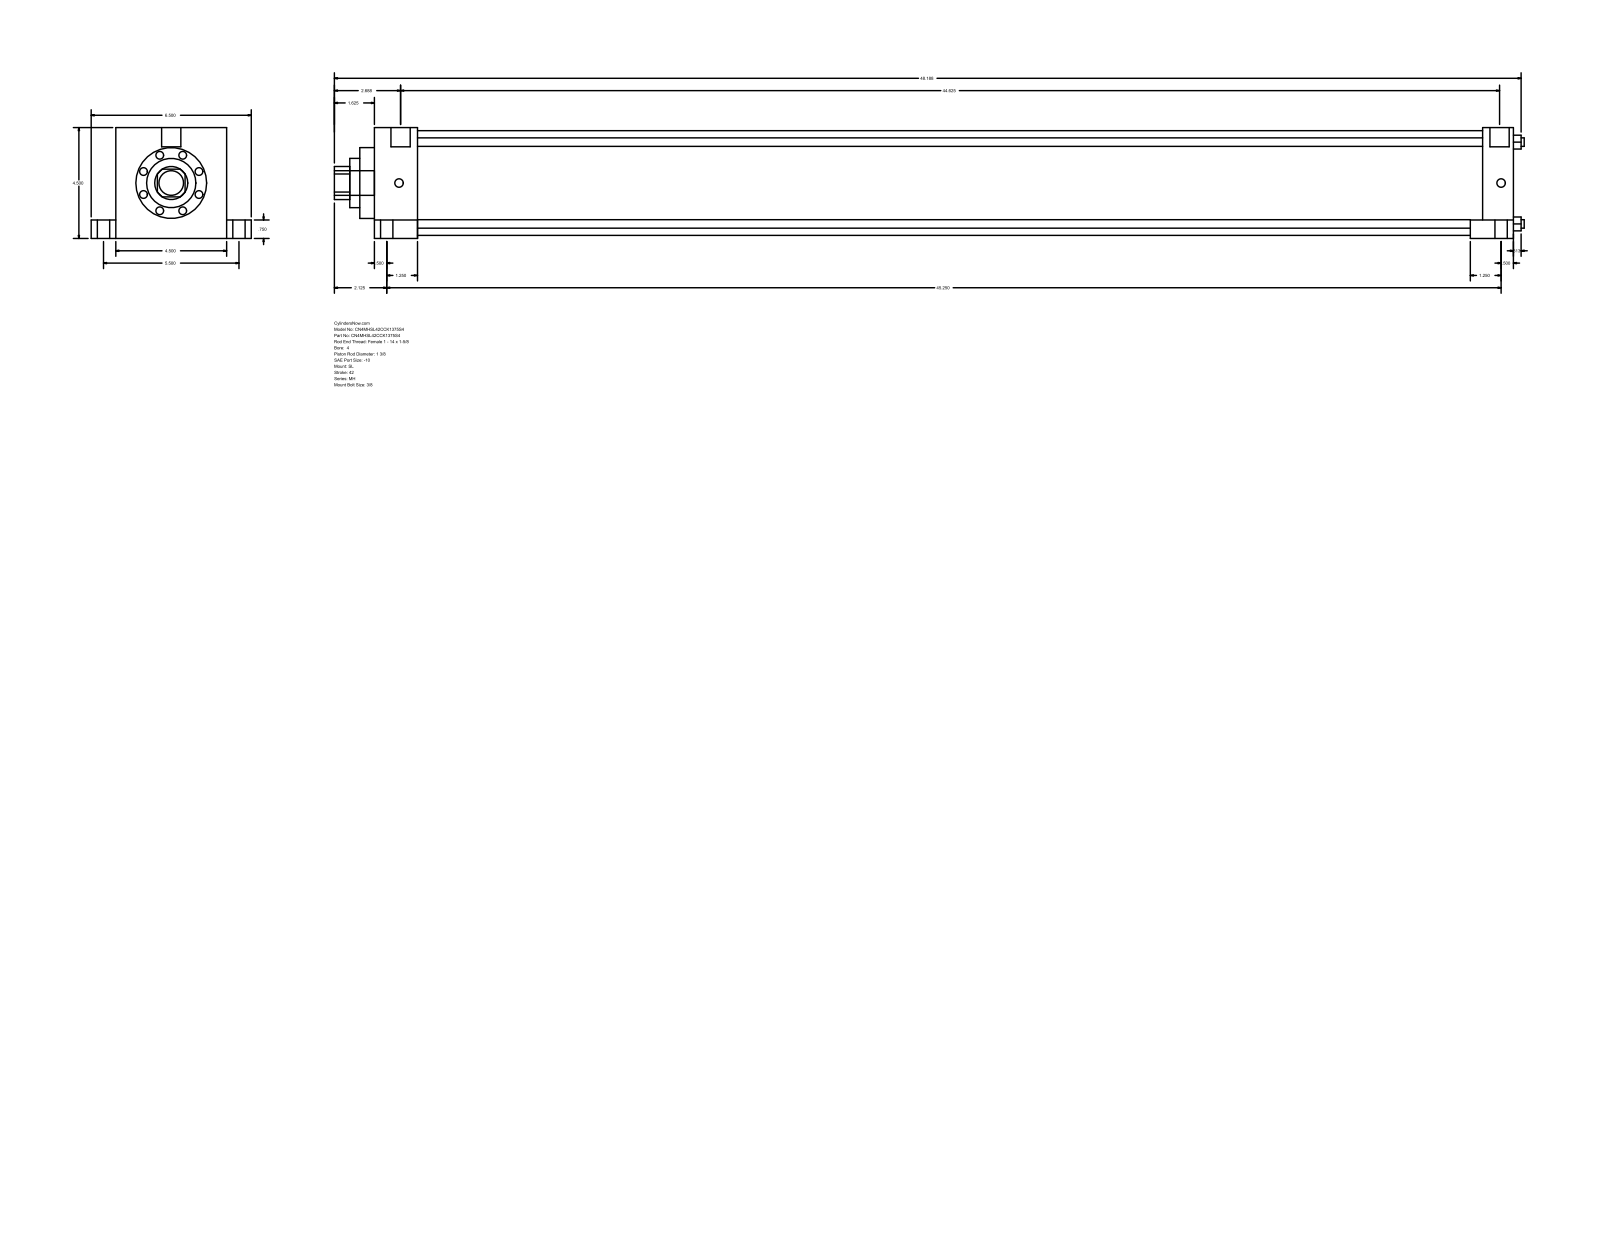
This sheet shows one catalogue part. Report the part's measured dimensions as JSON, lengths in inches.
{"part_name": "MH_SL__0400_1.375", "step_written_by": "GSSL Pune (CONFIG_CONTROL_DESIGN)", "units": "inches", "bodies": {"solids": 0, "faces": 110, "planar": 77, "cylindrical": 33, "other": 0}, "overall_size": [48.313, 6.5, 4.5], "round_holes": [[0.345, 4], [1.375, 1], [2, 1], [2.875, 1], [4.25, 1]], "round_bosses_or_shafts": [[0.75, 4], [0.5, 4], [0.344, 4], [0.781, 2], [1, 1]], "partial_cylinders_radius": [[0.672, 1]], "face_to_face_distances": [4.5, 46.25, 1.75, 44.5, 45, 43.25, 1.25, 1, 5.5, 0.75], "hole_center_spacings": [2.347, 3.32, 4.695]}
